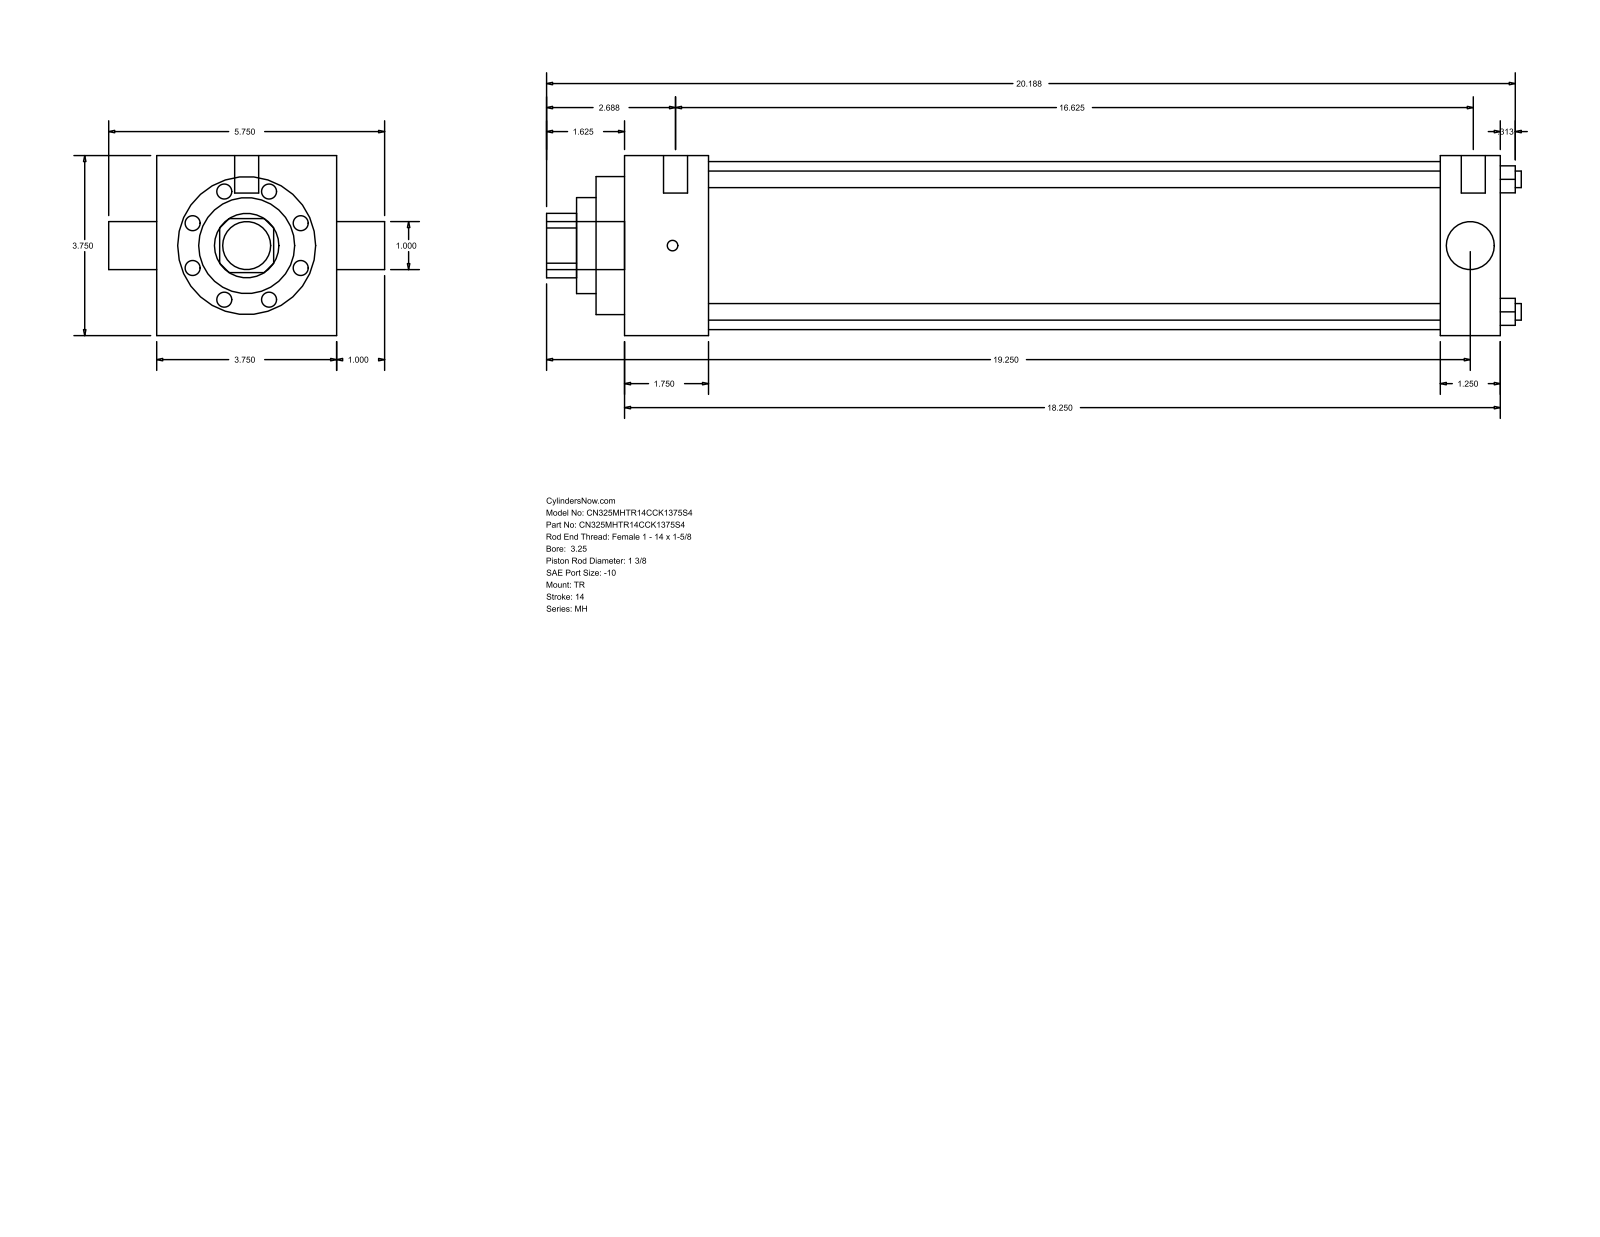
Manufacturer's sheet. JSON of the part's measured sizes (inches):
{"part_name": "MH_TR__0325_1.375", "step_written_by": "GSSL Pune (CONFIG_CONTROL_DESIGN)", "units": "inches", "bodies": {"solids": 0, "faces": 86, "planar": 61, "cylindrical": 25, "other": 0}, "overall_size": [20.313, 5.75, 3.75], "round_holes": [[0.345, 4], [1, 1], [1.375, 1], [2, 1], [2.875, 1], [3.5, 1]], "round_bosses_or_shafts": [[0.219, 3], [0.5, 2], [1, 1]], "partial_cylinders_radius": [[0.672, 1]], "face_to_face_distances": [3.75, 18.25, 1.75, 17, 15.25, 16.5, 1.25, 0.594, 2.344, 17.594], "hole_center_spacings": [1.952, 2.76, 3.903]}
